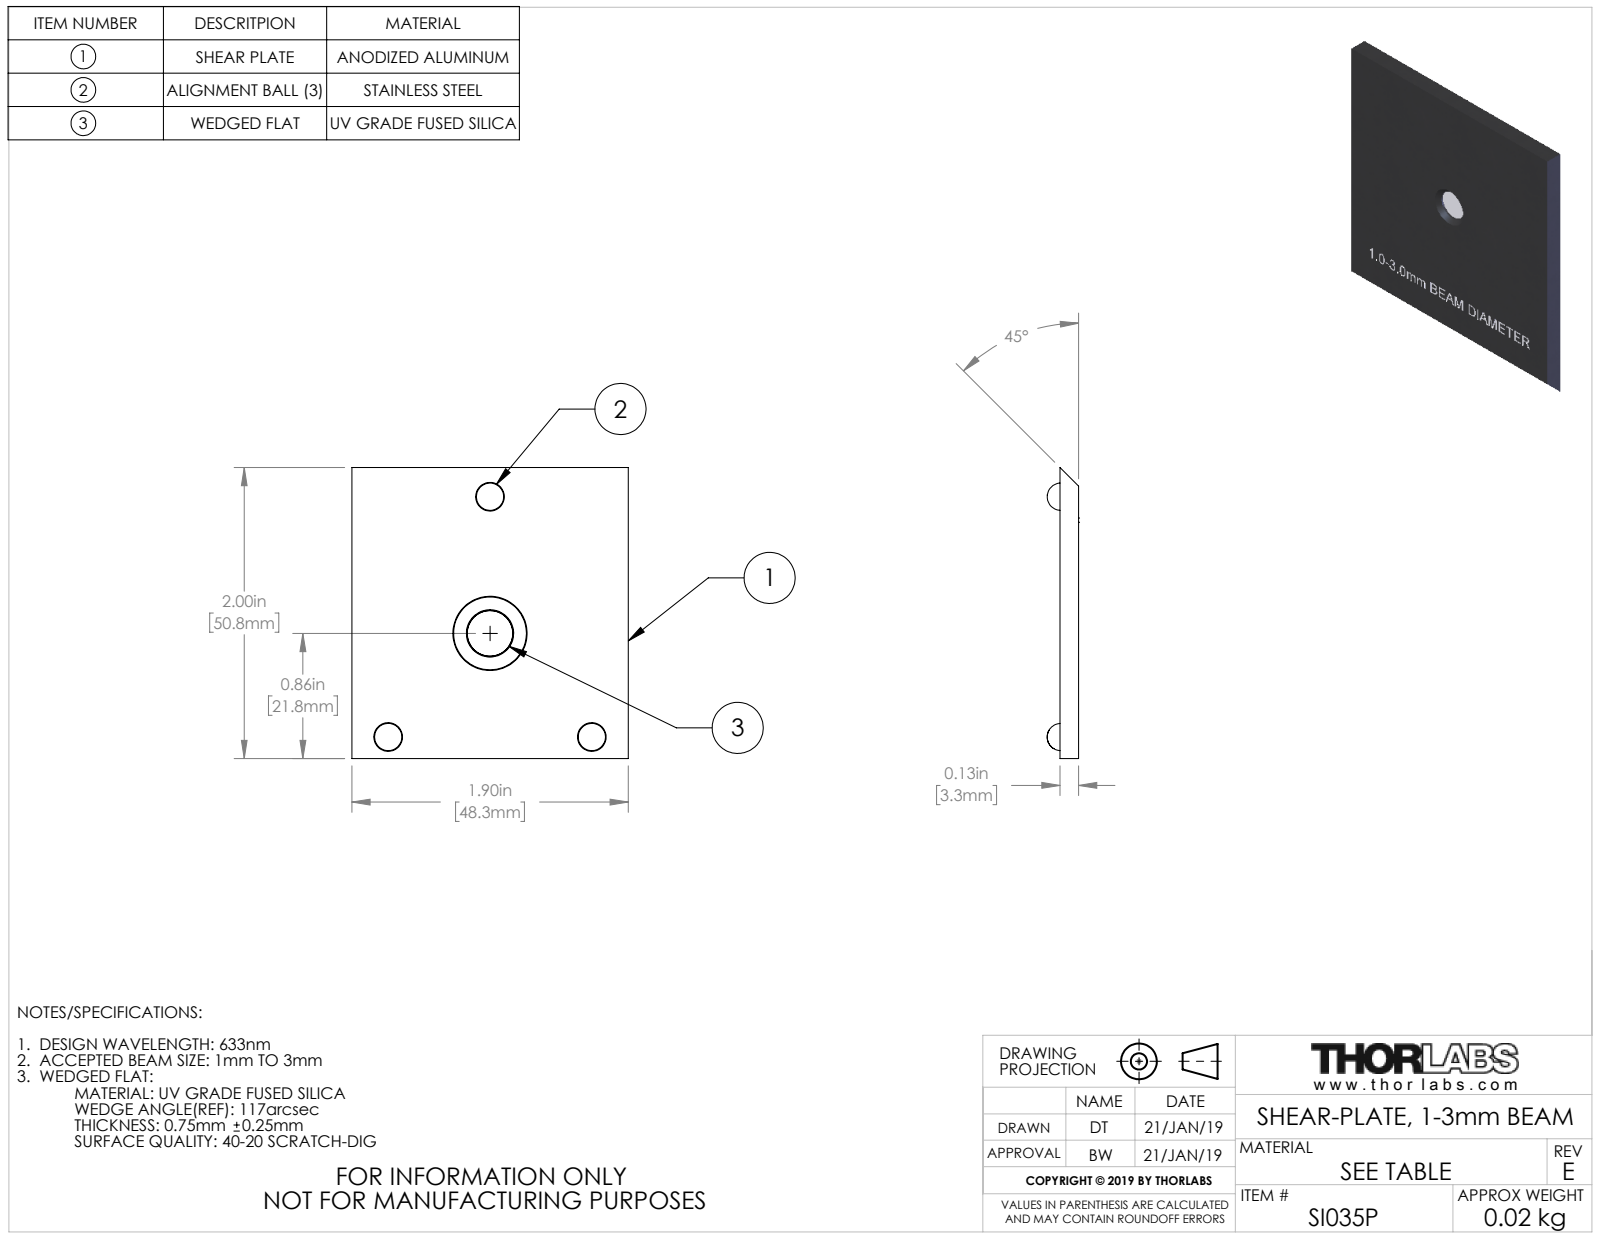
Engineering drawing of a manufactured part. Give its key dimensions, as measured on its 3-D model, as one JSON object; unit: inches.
{"part_name": "16654-E0W", "step_written_by": "SolidWorks 2018 (CONFIG_CONTROL_DESIGN)", "units": "inches", "bodies": {"solids": 5, "faces": 326, "planar": 206, "cylindrical": 14, "other": 106}, "overall_size": [2, 1.9, 0.216], "volume_in3": 0.46, "surface_area_in2": 9.184, "round_holes": [[0.187, 3], [0.213, 1], [0.315, 1], [0.5, 1]], "round_bosses_or_shafts": [[0.313, 1]], "face_to_face_distances": [0.128, 1.9, 0.049, 0.079, 0.025, 0.074, 0.054, 0.1, 0.028, 0.021], "hole_center_spacings": [0.998, 1.793, 0.939, 1.4]}
